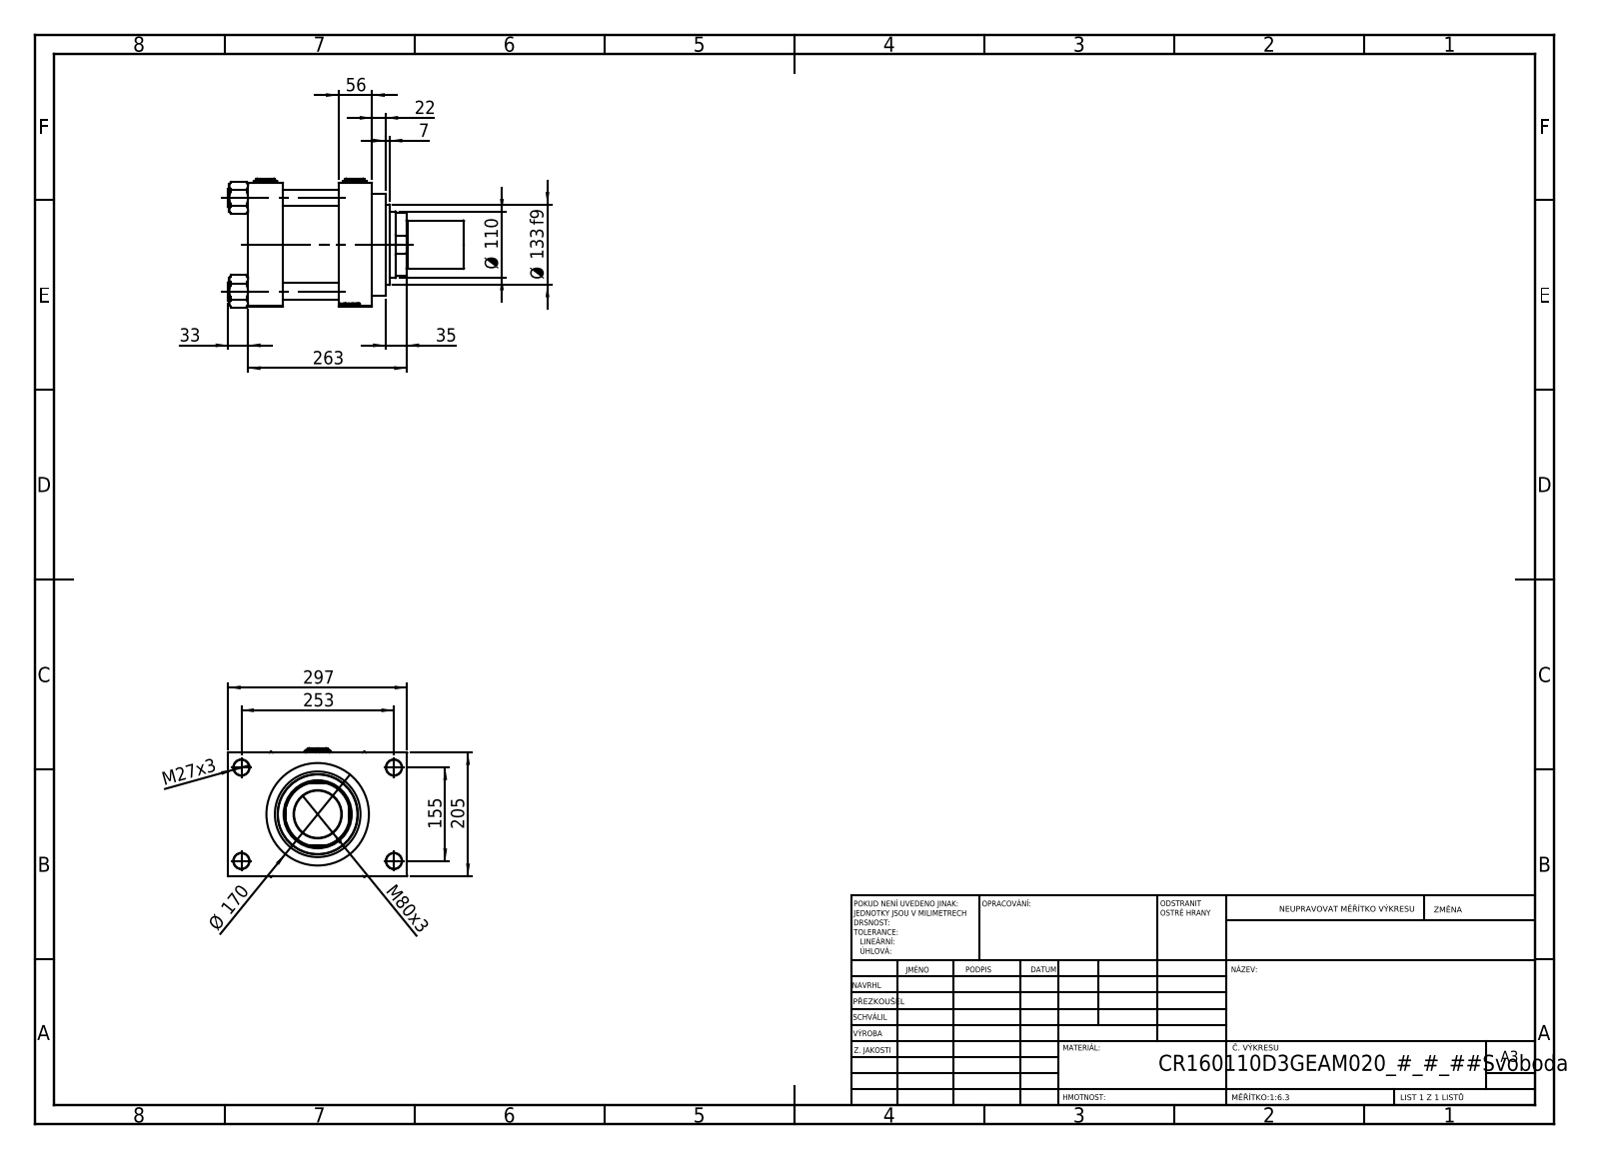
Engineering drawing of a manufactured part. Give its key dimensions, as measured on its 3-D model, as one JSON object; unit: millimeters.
{"part_name": "ROD_END_AH; V215CR_D_Body; Zatka_pro_OIL_PORT; V215CR_D_TYCINKA (+3 more)", "step_written_by": "SolidWorks 2019 (CONFIG_CONTROL_DESIGN)", "units": "millimeters", "bodies": {"solids": 14, "faces": 1267, "planar": 597, "cylindrical": 104, "other": 566}, "overall_size": [391, 297, 213.57], "volume_mm3": 8611000, "surface_area_mm2": 820301, "round_holes": [[26, 4], [27, 4], [7, 2], [33.24, 2], [45, 2], [78.5, 1], [110, 1], [113, 1], [120, 1], [142, 1], [160, 1]], "round_bosses_or_shafts": [[30, 4], [170, 1], [166, 1], [133, 1], [80, 1], [78, 1]], "partial_cylinders_radius": [[54, 1]], "face_to_face_distances": [205, 58, 150, 92, 148, 56, 206, 46, 251, 130], "hole_center_spacings": [49.05, 109.53, 148.35, 154.9, 162.53, 203.95, 256.13, 155]}
